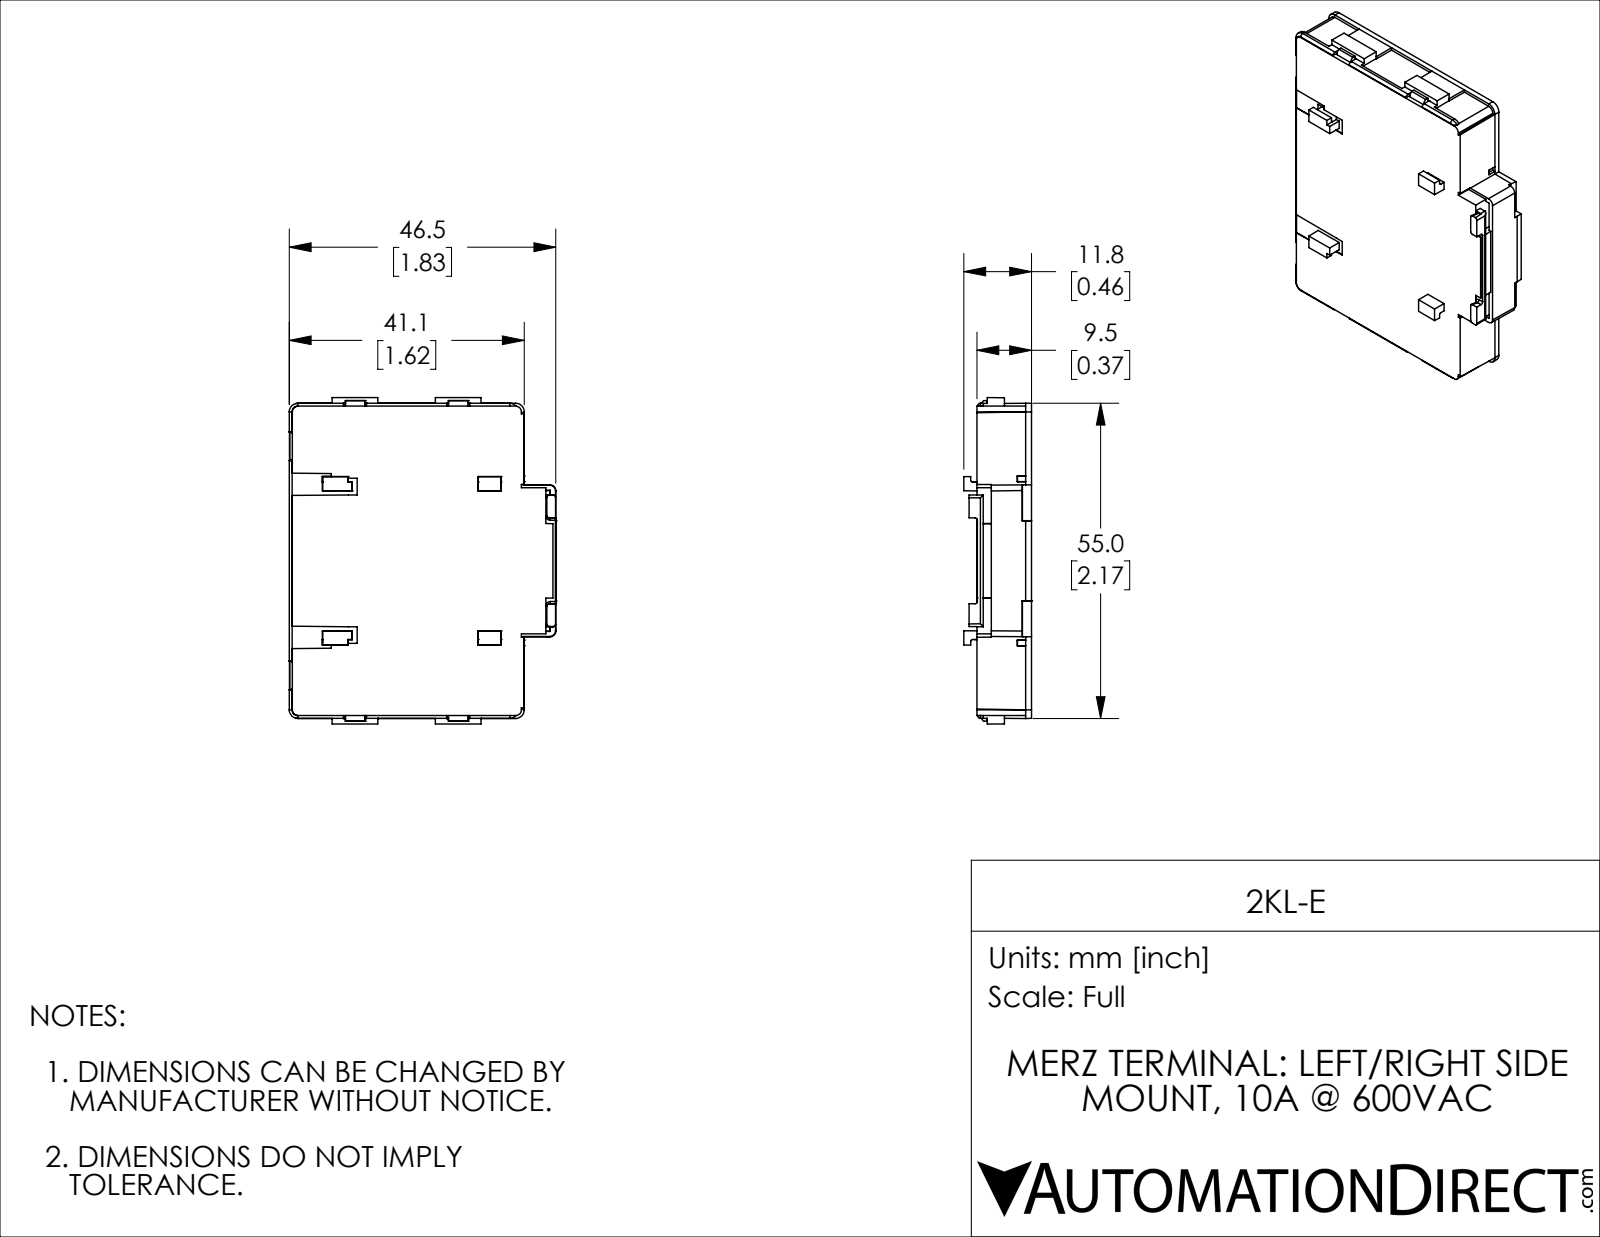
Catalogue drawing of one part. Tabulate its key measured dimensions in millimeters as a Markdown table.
| quantity | value |
| --- | --- |
| part name | 2KL-E |
| STEP written by | SolidWorks 2019 (AUTOMOTIVE_DESIGN) |
| units | millimeters |
| bodies | 1 solid, 375 faces (313 planar, 40 cylindrical, 22 other) |
| overall size | 57 × 46.6 × 11.8 |
| volume | 22 450 mm³ |
| surface area | 7 587 mm² |
| partial cylindrical surfaces (radius × count) | 0.4 × 7, 0.5 × 6, 1 × 6, 0.3 × 4, 0.8 × 2 |
| main face-to-face distances | 9.5, 1, 5.5, 54, 8.5, 8.4, 1.1, 55.9, 4.7, 14.2 |
